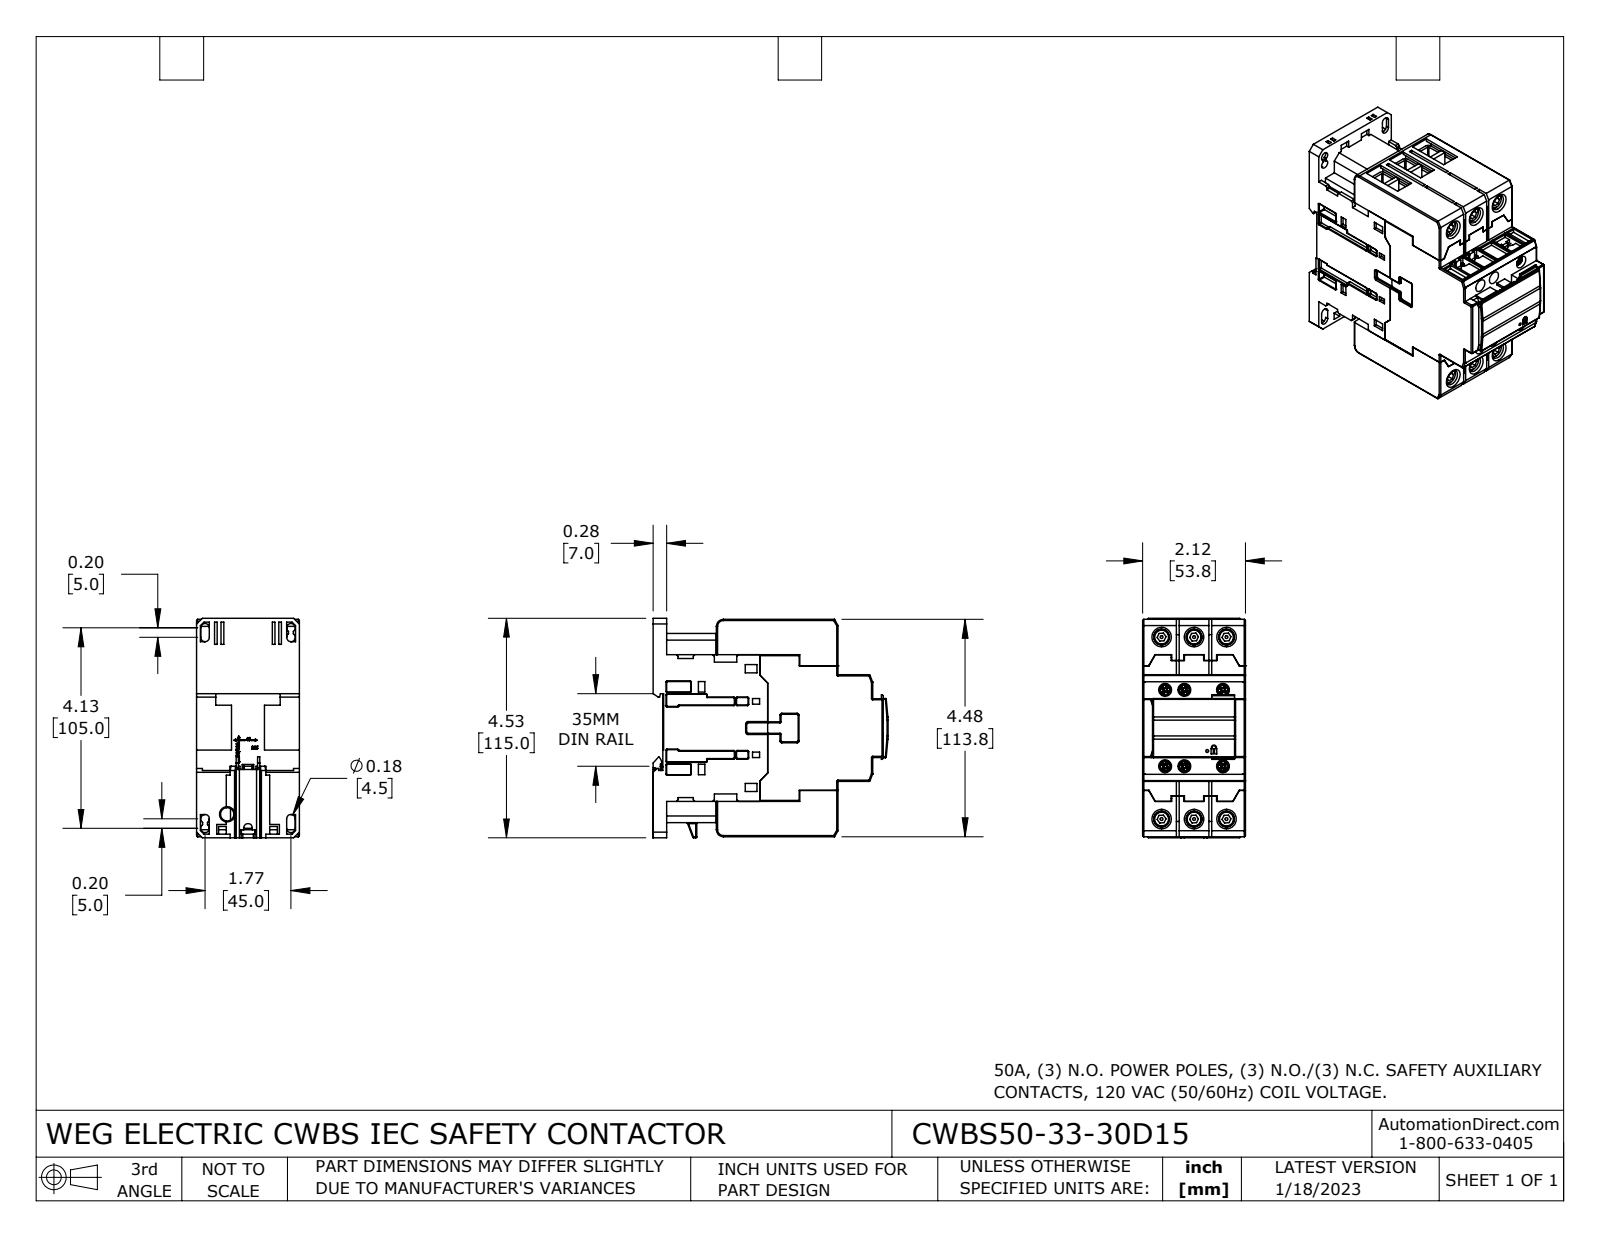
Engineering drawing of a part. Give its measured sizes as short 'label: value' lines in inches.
name: CWBS50-33-30D15
written by: SolidWorks 2021 (CONFIG_CONTROL_DESIGN)
unit: in
bodies: 37 solids, 2637 faces (1669 planar, 550 cylindrical, 418 other)
size: 4.846 × 4.528 × 2.118
volume: 33.67 in³; area: 209.3 in²
holes: 6× ⌀0.124, 6× ⌀0.197, 6× ⌀0.264, 6× ⌀0.323, 4× ⌀0.177, 2× ⌀0.125, 2× ⌀0.276, 1× ⌀0.059
bosses: 6× ⌀0.343, 6× ⌀0.236, 6× ⌀0.135
rounds: 89× R0.02, 69× R0.012, 48× R0.004, 42× R0.024, 18× R0.079, 5× R0.089, 3× R0.039, 3× R0.059
face distances: 0.059, 2.118, 0.669, 0.728, 3.024, 3.752, 0.108, 0.217, 3.811, 0.098
hole spacings: 0.669, 1.091, 1.241, 1.669, 2.665, 2.73, 2.949, 3.811
